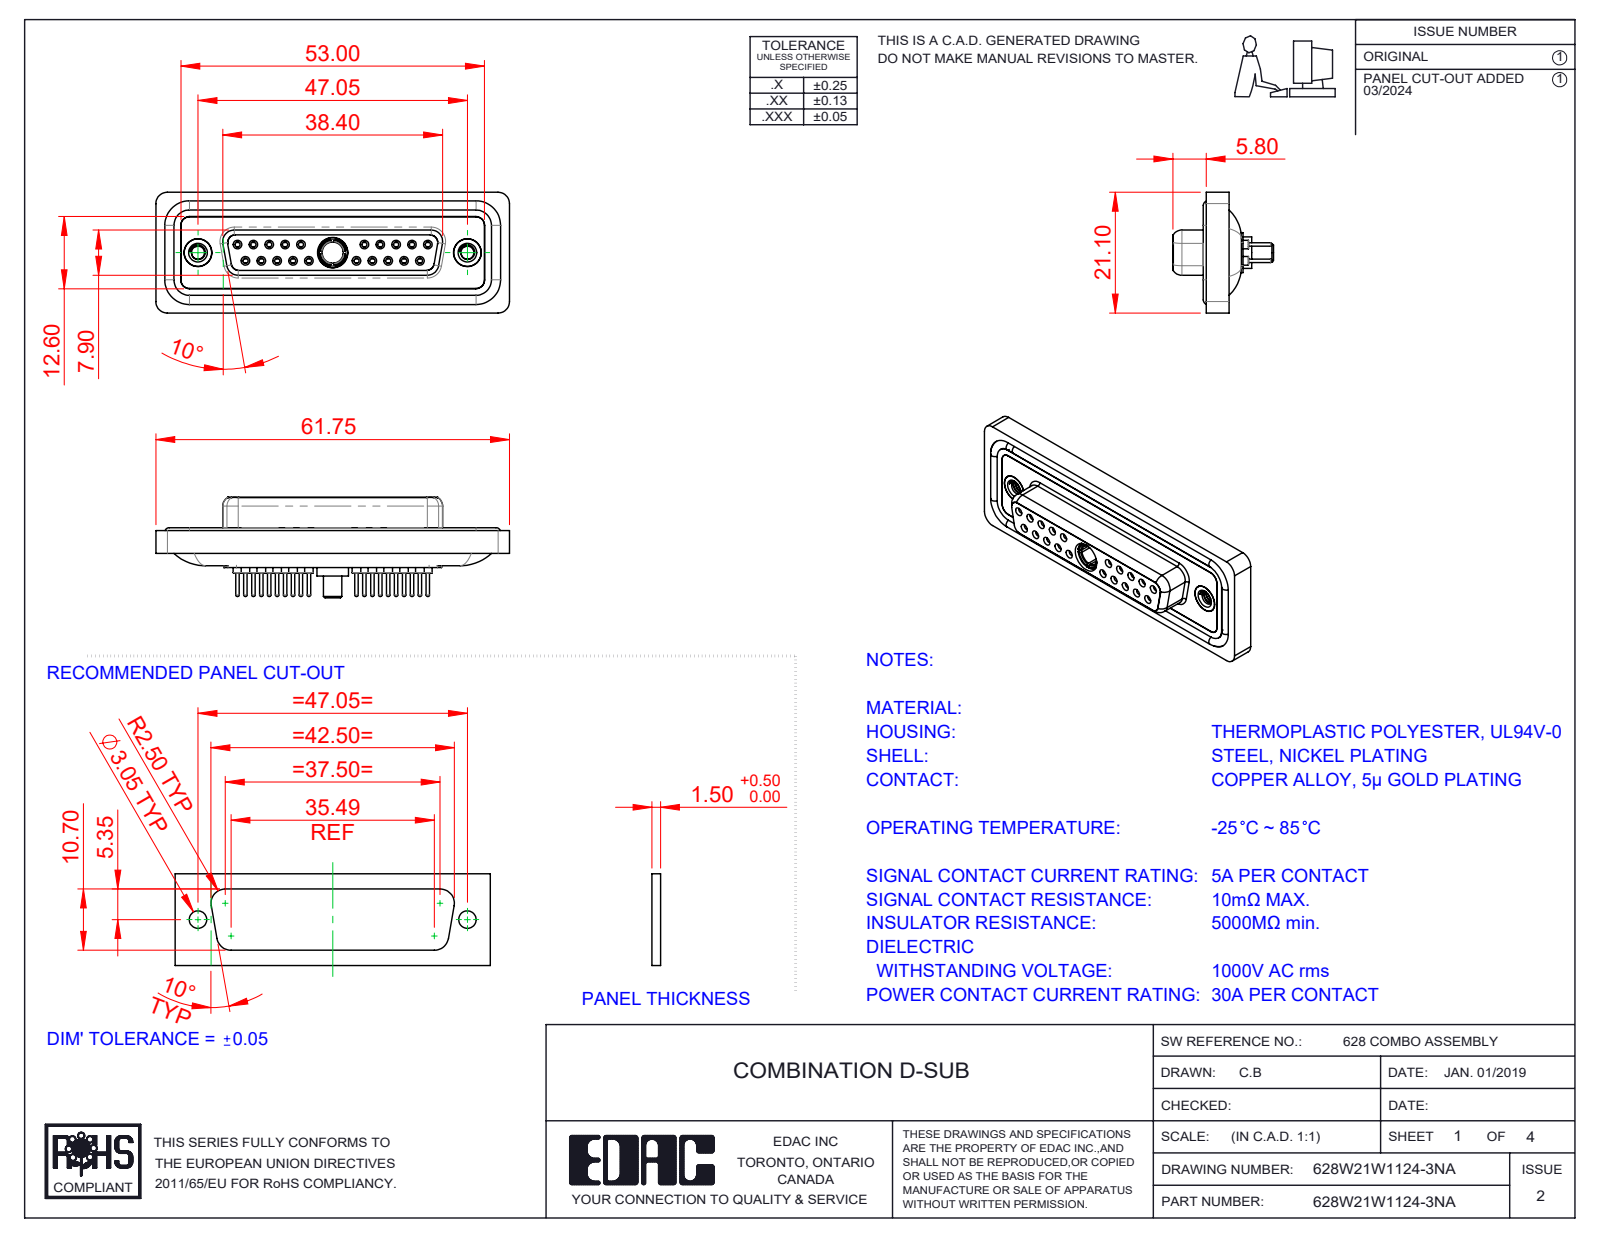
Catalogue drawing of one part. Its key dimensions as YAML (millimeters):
part_name: "Power Socket_30A S; 628Combo Waterproof Housing_25 Contacts; 628Combo Shell Rear_25 Contacts; 628Combo Threaded Rivet_A (+5 more)"
step_written_by: "SolidWorks 2023 (CONFIG_CONTROL_DESIGN)"
units: millimeters
bodies: {solids: 29, faces: 1558, planar: 434, cylindrical: 593, other: 531}
overall_size: [61.75, 21.1, 17.55]
volume: 8383
surface_area: 14004
round_holes:
  - {diameter: 0.9, count: 20}
  - {diameter: 1.1, count: 20}
  - {diameter: 1.5, count: 20}
  - {diameter: 2, count: 20}
  - {diameter: 1.6, count: 10}
  - {diameter: 1.7, count: 10}
  - {diameter: 4.85, count: 3}
  - {diameter: 2.26, count: 2}
  - {diameter: 4, count: 2}
  - {diameter: 4.05, count: 2}
  - {diameter: 5, count: 2}
  - {diameter: 3.7, count: 1}
round_bosses_or_shafts:
  - {diameter: 2.2, count: 20}
  - {diameter: 0.6, count: 20}
  - {diameter: 1.6, count: 14}
  - {diameter: 4.95, count: 2}
  - {diameter: 4.8, count: 2}
  - {diameter: 5.5, count: 1}
  - {diameter: 5.2, count: 1}
  - {diameter: 4.96, count: 1}
partial_cylinders:
  - {radius: 1.5, count: 22}
  - {radius: 2, count: 18}
  - {radius: 1.35, count: 8}
  - {radius: 1.6, count: 8}
  - {radius: 0.25, count: 4}
  - {radius: 0.5, count: 4}
  - {radius: 0.6, count: 4}
  - {radius: 0.65, count: 4}
face_to_face_distances: [0.4, 1.8, 7.45, 6.6, 5.65, 0.5, 1.6, 7.05, 2.9, 1.1]
hole_center_spacings: [3.16, 2.77, 5.54, 5.03, 8.31, 7.48, 16.62, 19.39]
